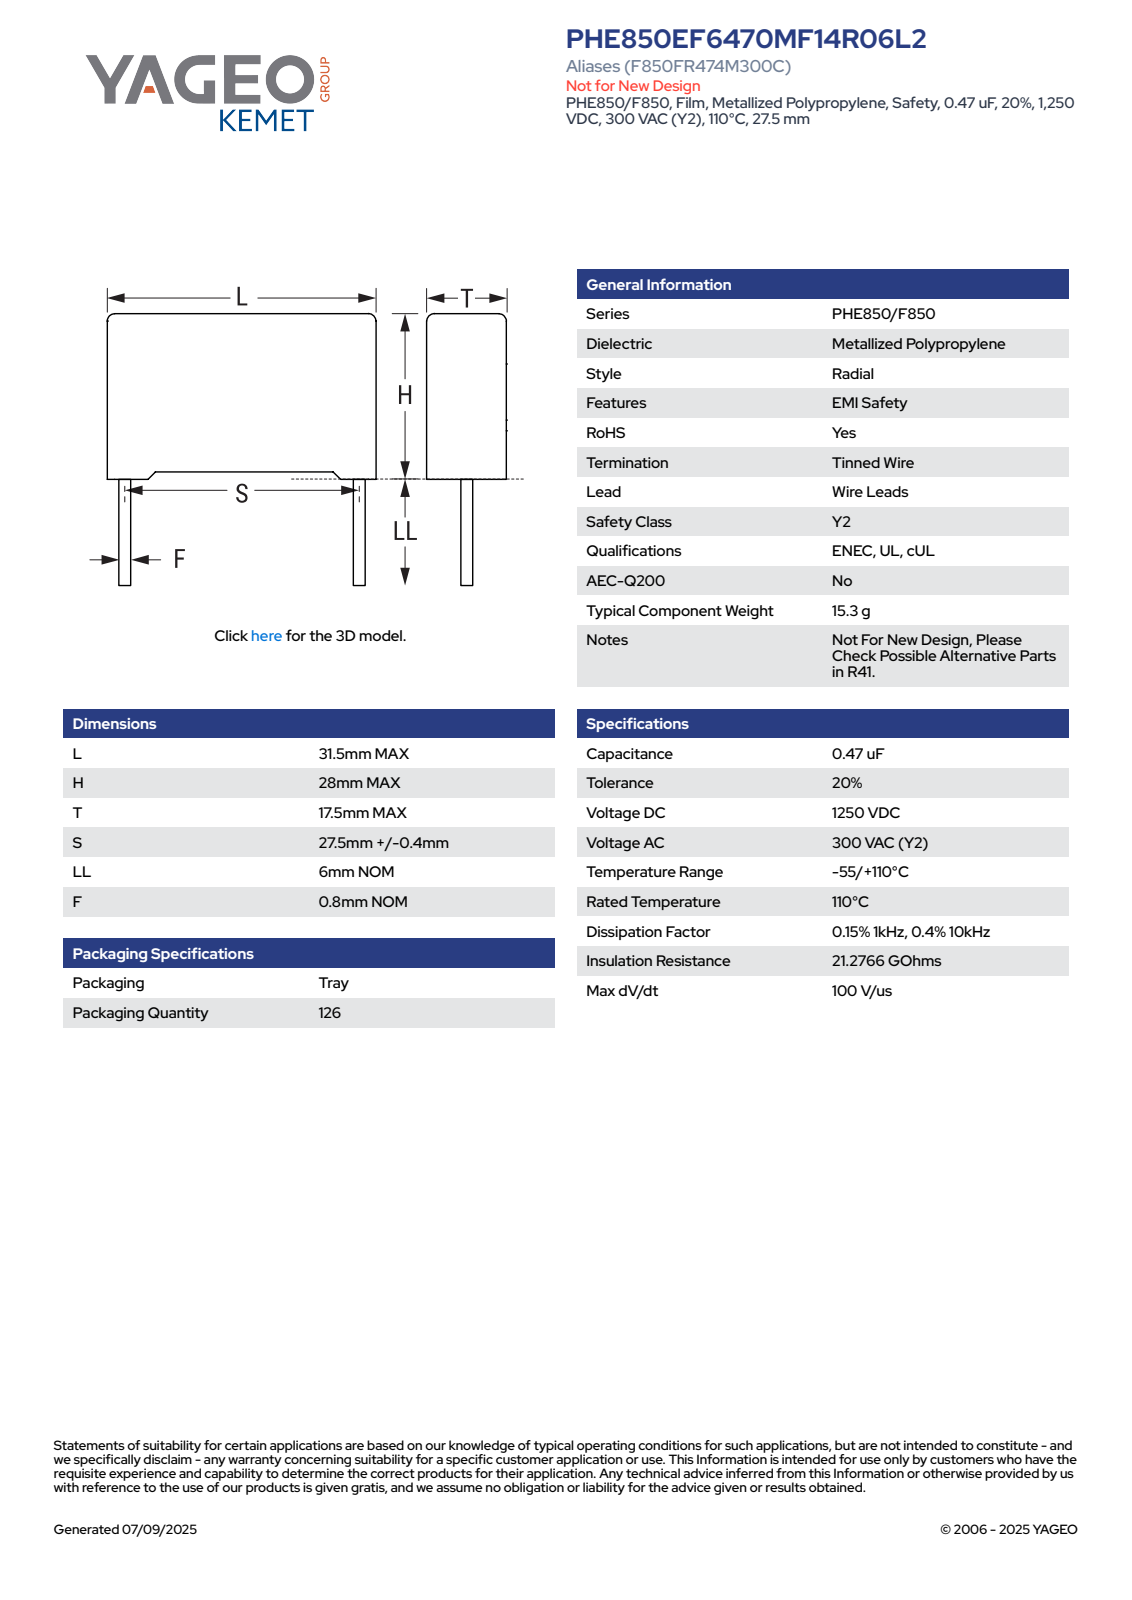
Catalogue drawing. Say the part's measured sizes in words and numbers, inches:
The part is named "CFR_RB2_31.5X28X17.5_L31.5H28T17.5S27.5LL6F0.8". Its 3-D file was written by "SolidWorks 2021 (AUTOMOTIVE_DESIGN)". It is 4 solids with 85 faces: 77 planar, 8 cylindrical and 0 other. Overall it measures 1.339 by 1.24 by 0.689 inches. Its volume is 0.914 cubic inches and its surface area 6.082 square inches. Round bosses or shafts: 2 of diameter 0.031. Partial cylindrical surfaces (rounded edges, fillets, slot ends): 4 of radius 0.02. The main face-to-face distances are 0.689, 1.24, 1.064, 1.073, 0.038, 0.03, 1.102, 0.041, 1.199, 0.689.
